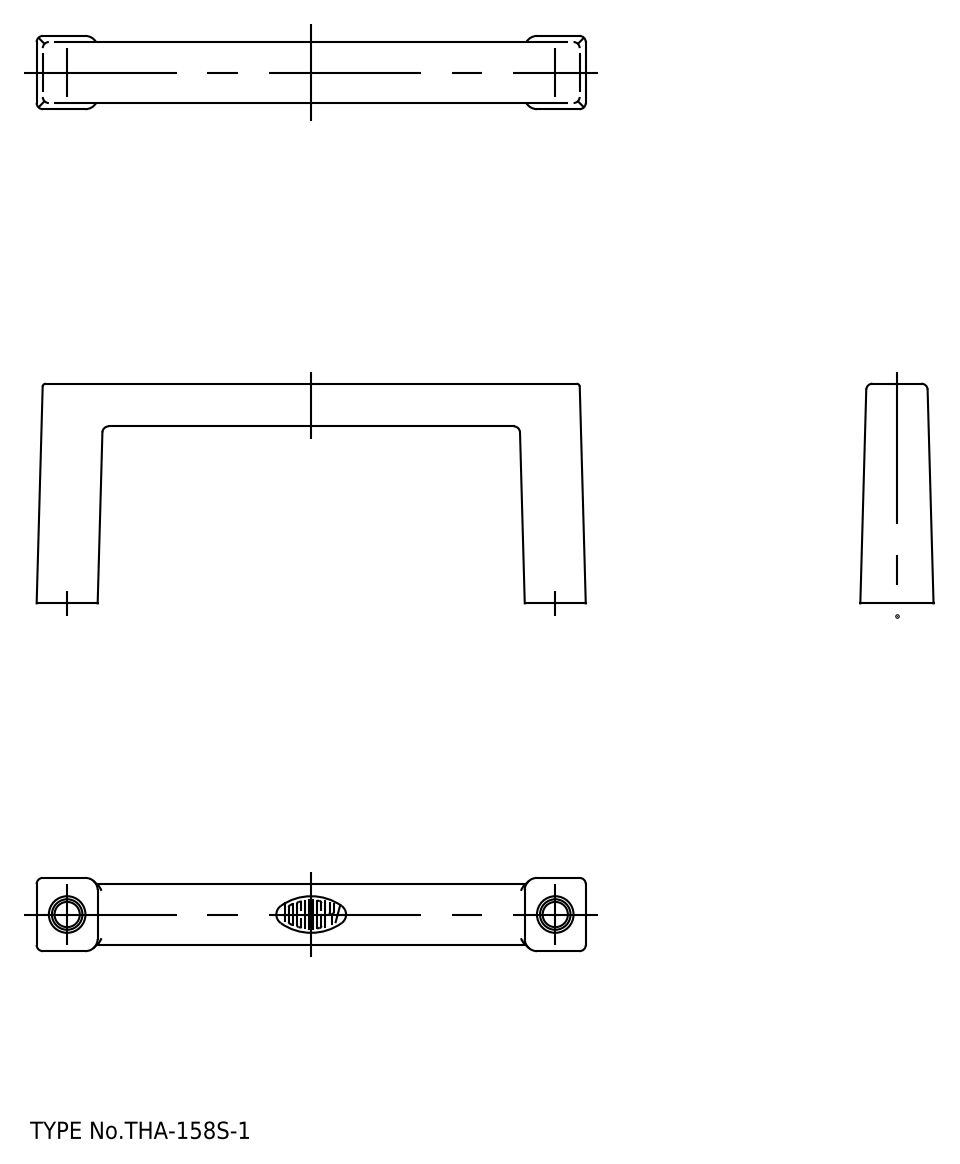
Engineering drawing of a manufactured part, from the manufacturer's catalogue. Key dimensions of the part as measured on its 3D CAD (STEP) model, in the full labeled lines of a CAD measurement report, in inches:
STEP written by: spGate 16.7.1 (AUTOMOTIVE_DESIGN)
Units: inches
Bodies: 1 solid, 48 faces (12 planar, 24 cylindrical, 12 other)
Overall size (bounding box): 3.543 × 1.417 × 0.472
Volume: 0.733 in³ · Surface area: 8.776 in²
Round holes (diameter × count): ⌀0.197 ×2
Partial cylindrical surfaces — rounded edges, fillets, slot ends (radius × count): R0.039 ×14, R0.079 ×6
Main face-to-face distances: 0.276, 0.393, 0.394, 1.417, 1.142, 0.945, 0.669, 0.472
Hole centre spacings: 3.15
